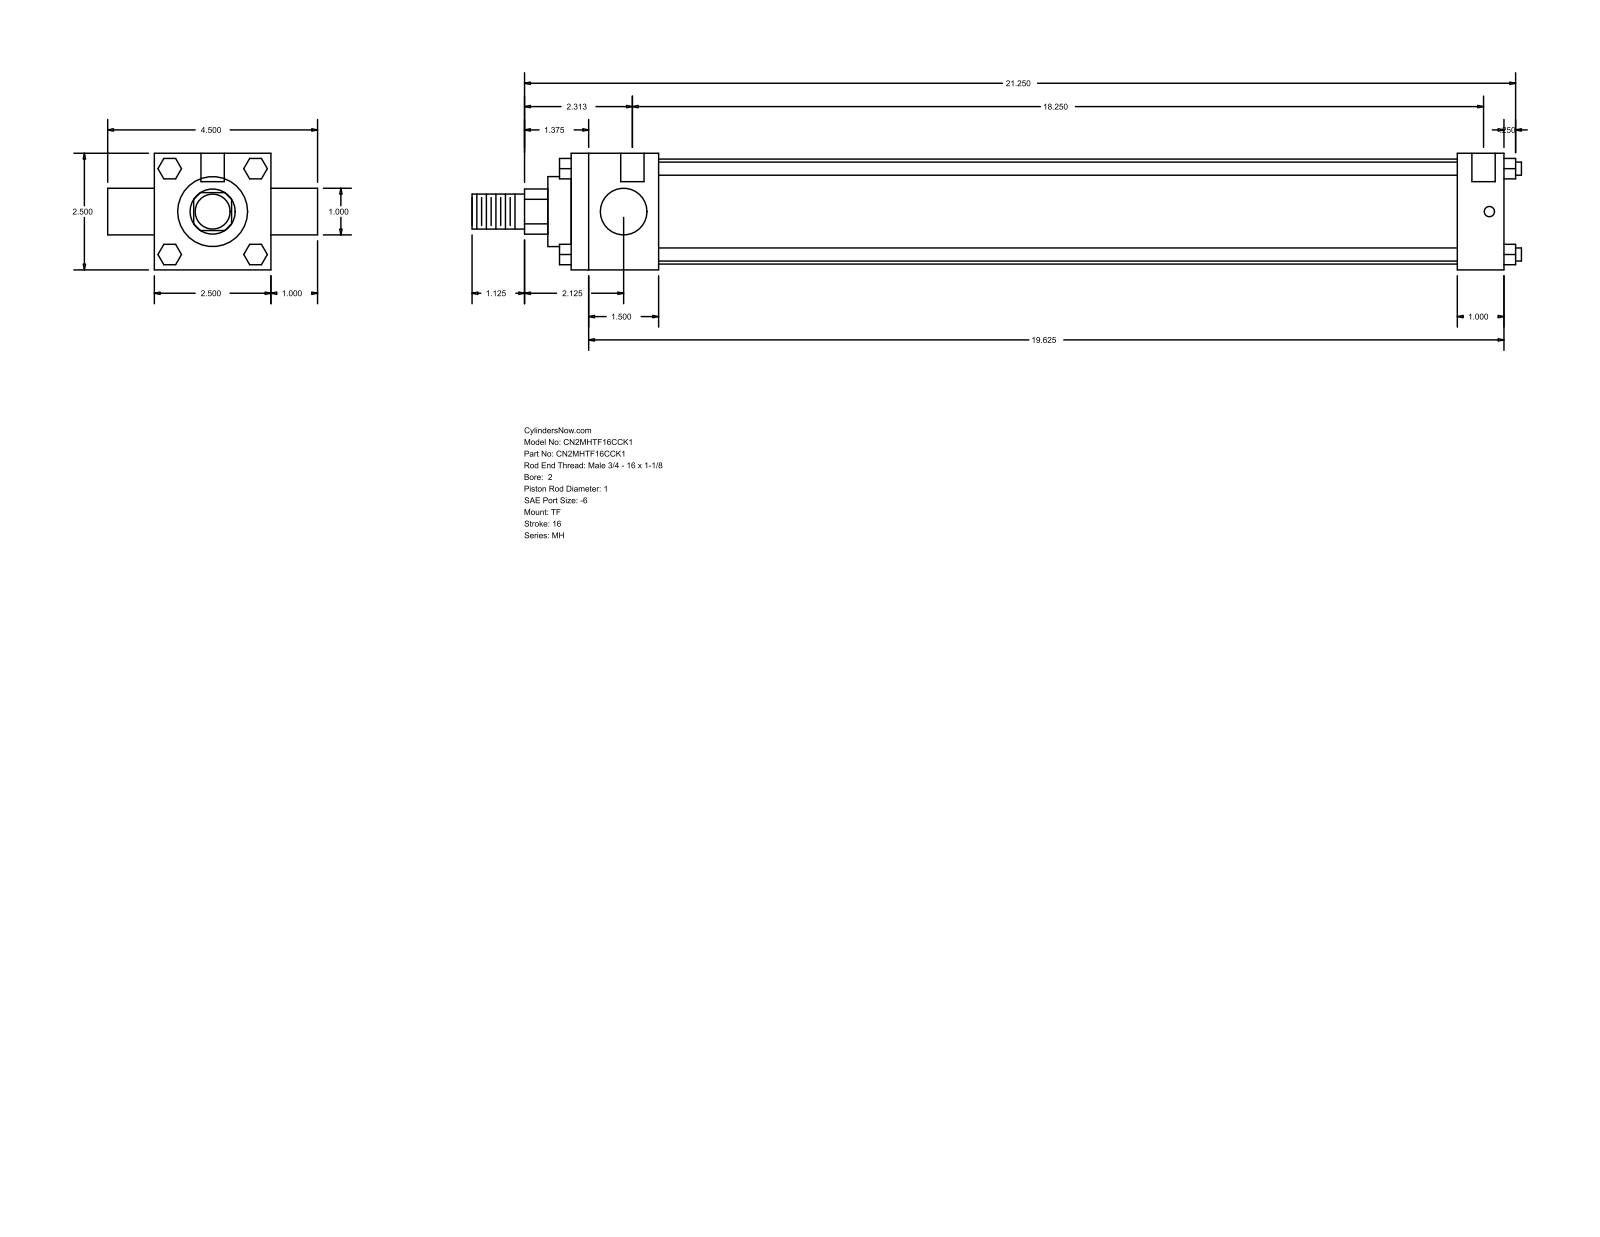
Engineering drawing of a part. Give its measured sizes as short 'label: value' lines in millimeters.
name: MH_TF__0200_1
written by: GSSL Pune (CONFIG_CONTROL_DESIGN)
unit: mm
bodies: 0 solids, 120 faces (92 planar, 28 cylindrical, 0 other)
size: 571.5 × 114.3 × 63.5
holes: 3× ⌀5.56, 2× ⌀12.7
bosses: 4× ⌀7.14, 2× ⌀25.4, 1× ⌀57.15, 1× ⌀38.1, 1× ⌀19.05
rounds: 1× R12.29
face distances: 63.5, 508, 25.4, 47.63, 482.6, 434.97, 460.37, 88.9, 520.7, 6.35
hole spacings: 3.17, 4.76, 463.55, 466.72, 468.31, 471.48
